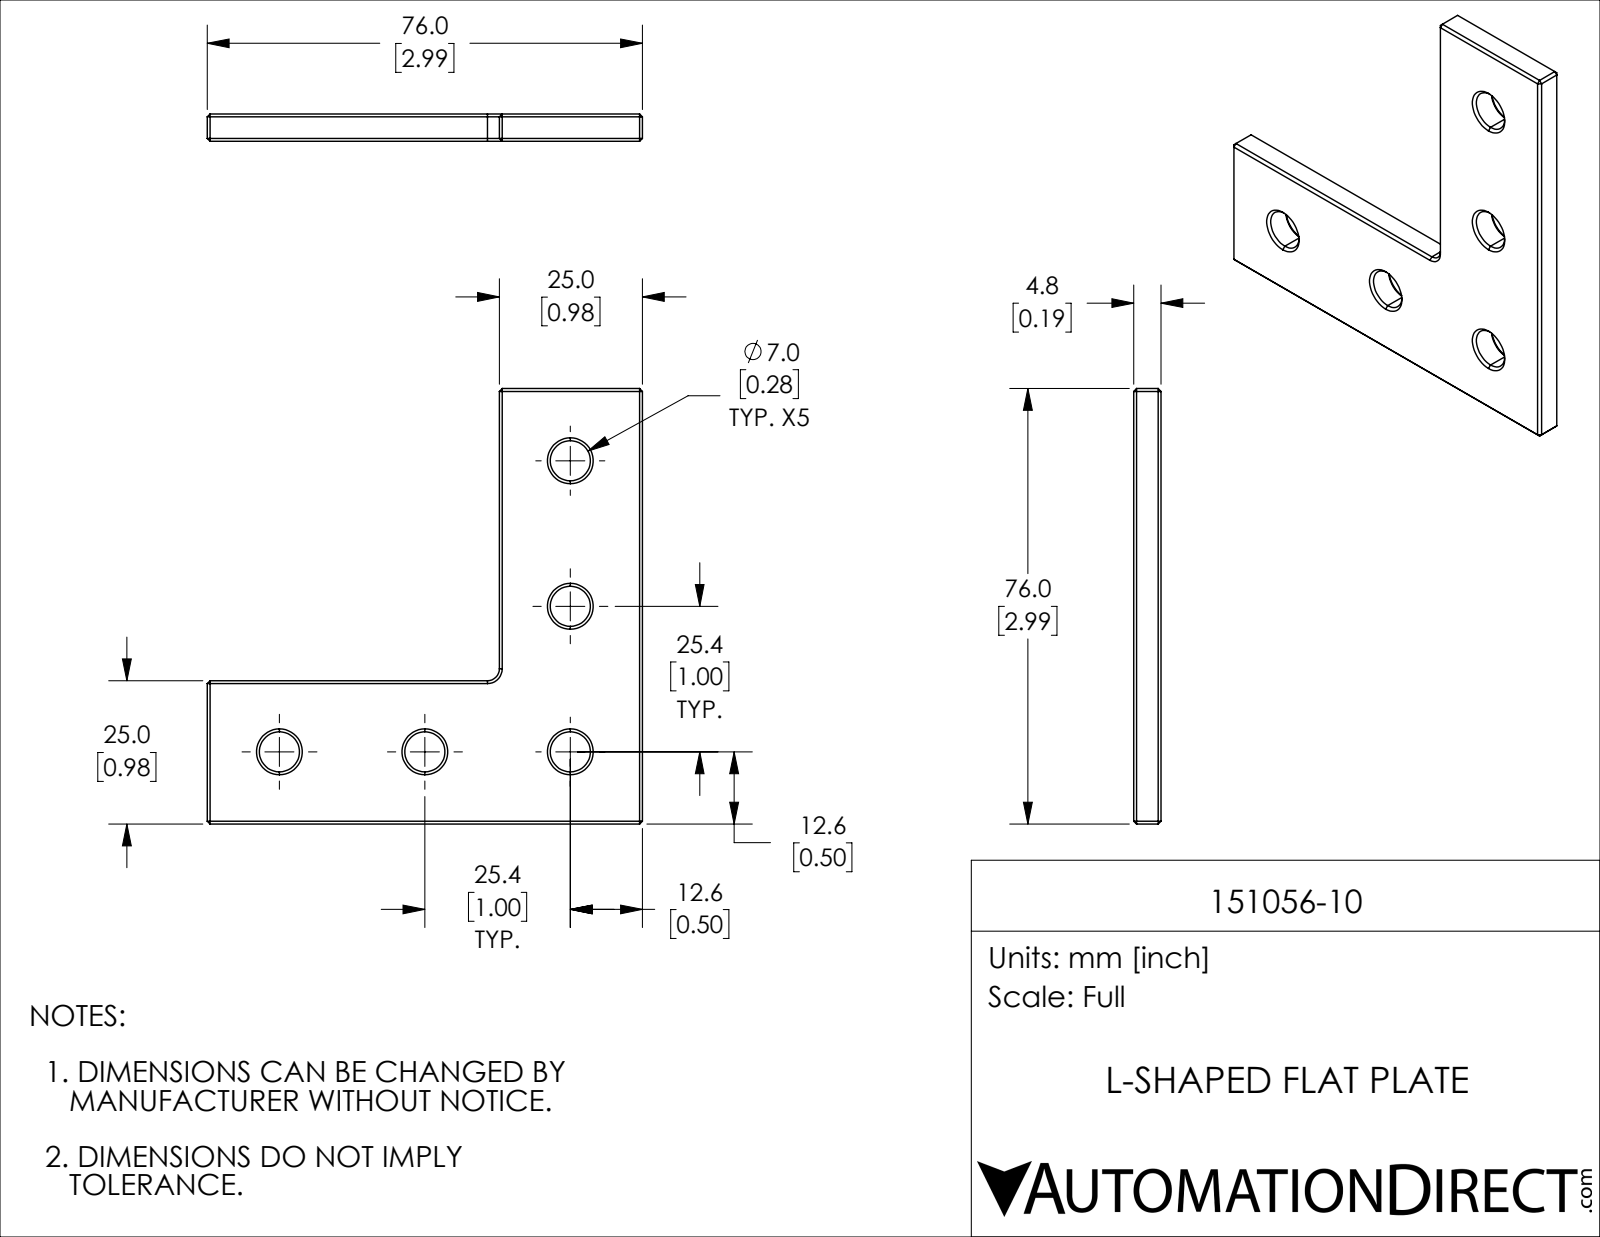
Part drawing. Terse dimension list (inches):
name: 151056-10
written by: SolidWorks 2024 (CONFIG_CONTROL_DESIGN)
unit: in
bodies: 1 solid, 68 faces (35 planar, 11 cylindrical, 22 other)
size: 2.992 × 2.992 × 0.187
volume: 0.861 in³; area: 11.92 in²
holes: 5× ⌀0.276
rounds: 1× R0.082
face distances: 0.187, 0.984, 2.008, 2.992, 0.801, 0.8, 2.22, 1.419, 1.42, 2.783
hole spacings: 1, 2, 2.236, 1.414, 2.828
